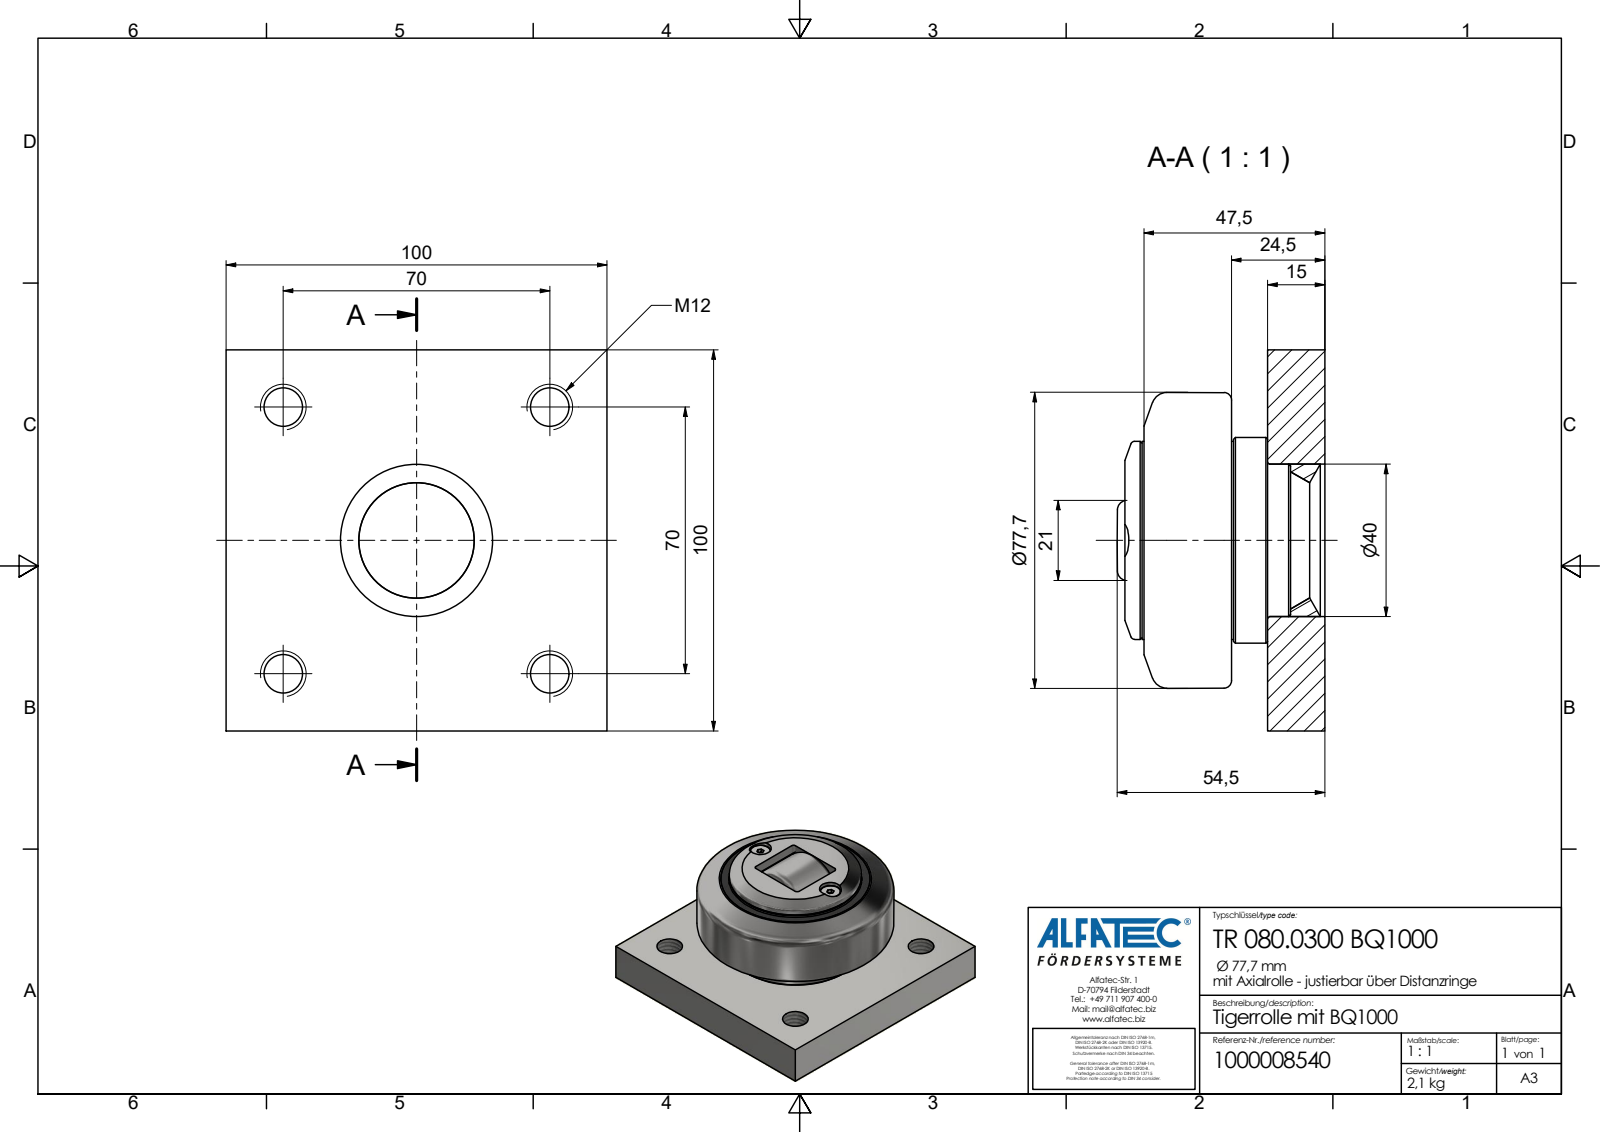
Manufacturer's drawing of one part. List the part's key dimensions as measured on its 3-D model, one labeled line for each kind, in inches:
Part name (STEP PRODUCT): TR 080.0300 BQ1000_Kontur
STEP written by: Autodesk Inventor 2020 (AP242_MANAGED_MODEL_BASED_3D_ENGINEERING_MIM_LF)
Units: inches
Bodies: 1 solid, 99 faces (46 planar, 32 cylindrical, 21 other)
Overall size (bounding box): 3.937 × 3.937 × 2.146
Volume: 16.9 in³ · Surface area: 65.77 in²
Round holes (diameter × count): ⌀0.398 ×4, ⌀0.177 ×2, ⌀0.339 ×2, ⌀1.575 ×1, ⌀1.819 ×1
Round bosses / shafts (diameter × count): ⌀0.307 ×2, ⌀0.157 ×2, ⌀2.126 ×1, ⌀2.047 ×1, ⌀1.291 ×1
Partial cylindrical surfaces — rounded edges, fillets, slot ends (radius × count): R0.039 ×4, R0.315 ×1, R0.354 ×1, R0.413 ×1
Main face-to-face distances: 0.591, 3.937, 0.965, 0.374, 0.02, 0.925, 1.87, 1.28, 0.906, 1.89
Hole centre spacings: 1.507, 1.949, 2.55, 2.756, 0.768, 3.897, 1.535
